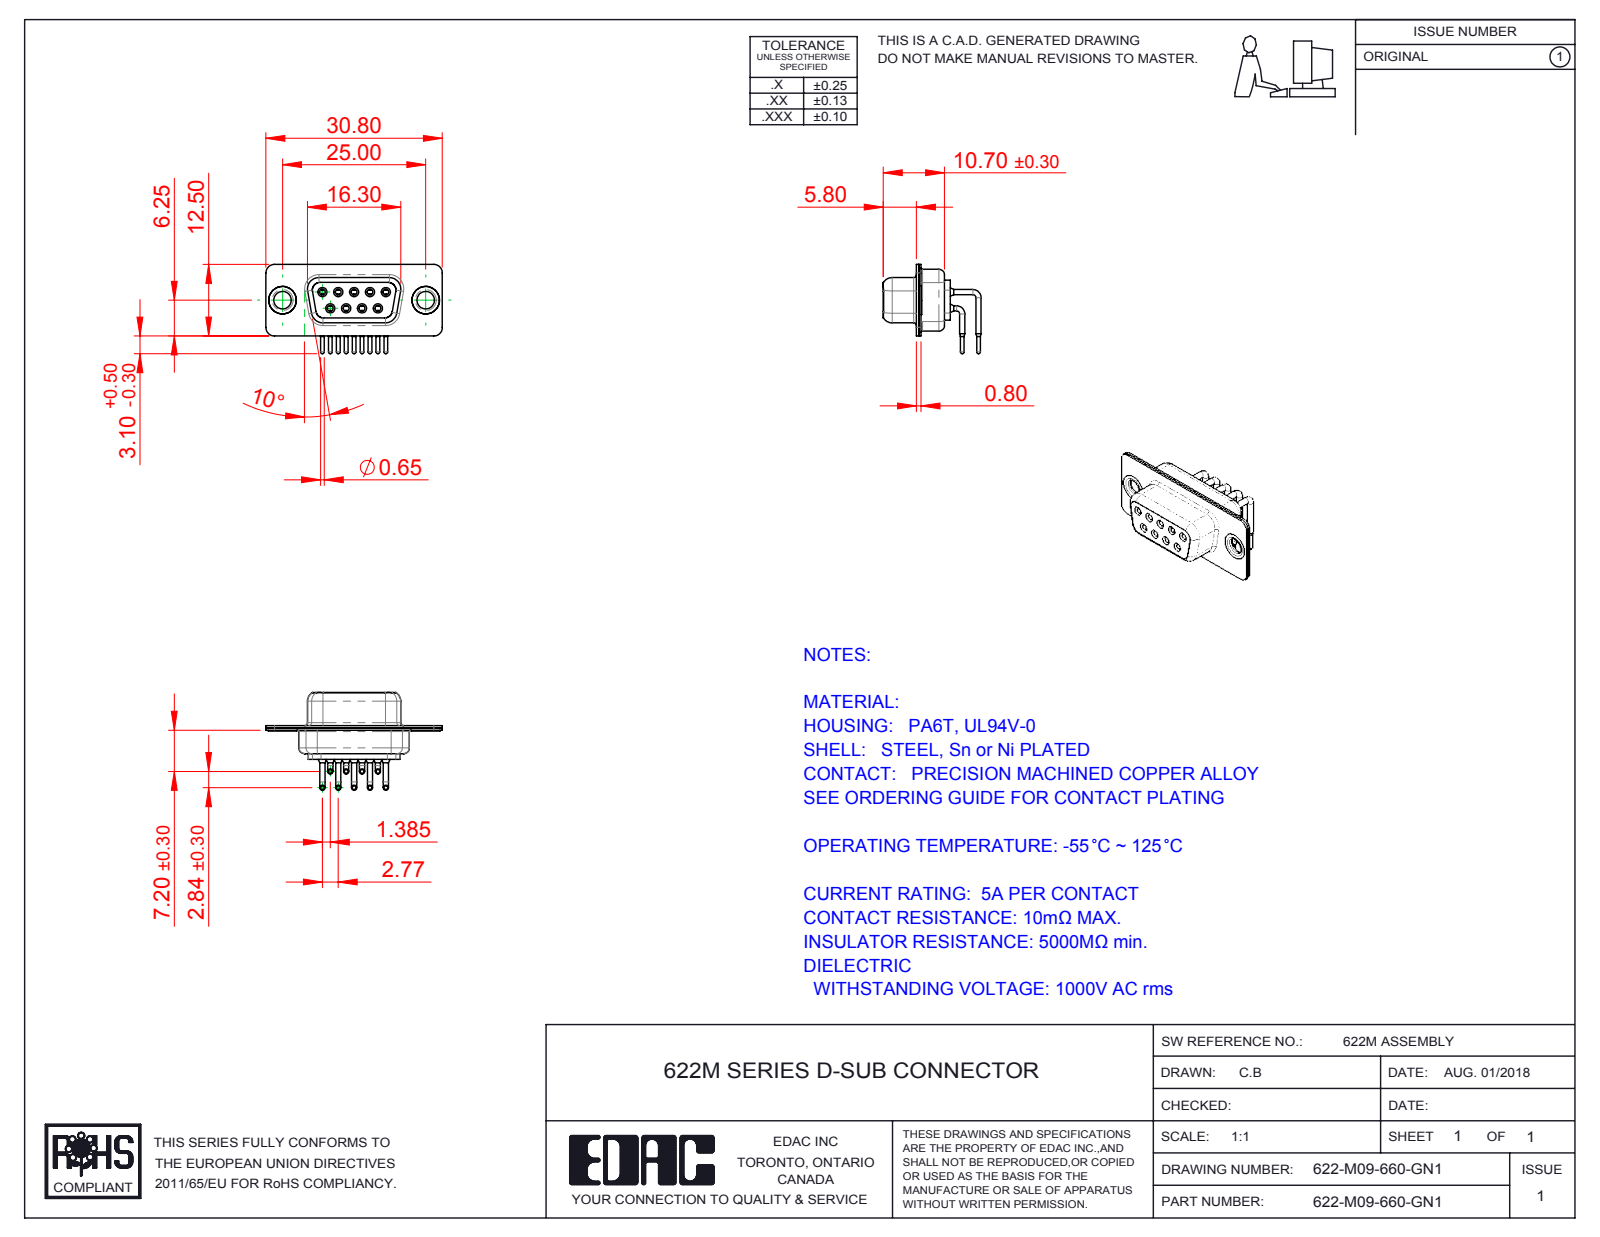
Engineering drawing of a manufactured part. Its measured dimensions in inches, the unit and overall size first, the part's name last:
Units: inches
Overall size (bounding box): 1.213 × 0.673 × 0.614
Round holes (diameter × count): ⌀0.039 ×9, ⌀0.043 ×9, ⌀0.067 ×9, ⌀0.071 ×9, ⌀0.079 ×9, ⌀0.12 ×2, ⌀0.157 ×2, ⌀0.189 ×2
Round bosses / shafts (diameter × count): ⌀0.035 ×18, ⌀0.063 ×9, ⌀0.059 ×9, ⌀0.026 ×9, ⌀0.197 ×2, ⌀0.193 ×2, ⌀0.14 ×2
Partial cylindrical surfaces — rounded edges, fillets, slot ends (radius × count): R0.059 ×16, R0.079 ×12, R0.053 ×8, R0.063 ×8, R0.01 ×4, R0.02 ×4, R0.024 ×4, R0.026 ×4
Main face-to-face distances: 0.016, 0.031, 0.057, 0.352, 0.091, 0.244, 0.335, 0.075, 0.033, 0.368
Hole centre spacings: 0.124, 0.109, 0.218, 0.198, 0.198, 0.327, 0.28, 0.294
Volume: 0.102 in³ · Surface area: 6.834 in²
Bodies: 14 solids, 730 faces (202 planar, 328 cylindrical, 200 other)
Part name (STEP PRODUCT): 622-M09-660-GN1; 622M Thru Hole Rivet; 622M Contact Row 2; 622M Shell Rear_09 Contacts (+3 more)
STEP written by: SolidWorks 2016 (CONFIG_CONTROL_DESIGN)
